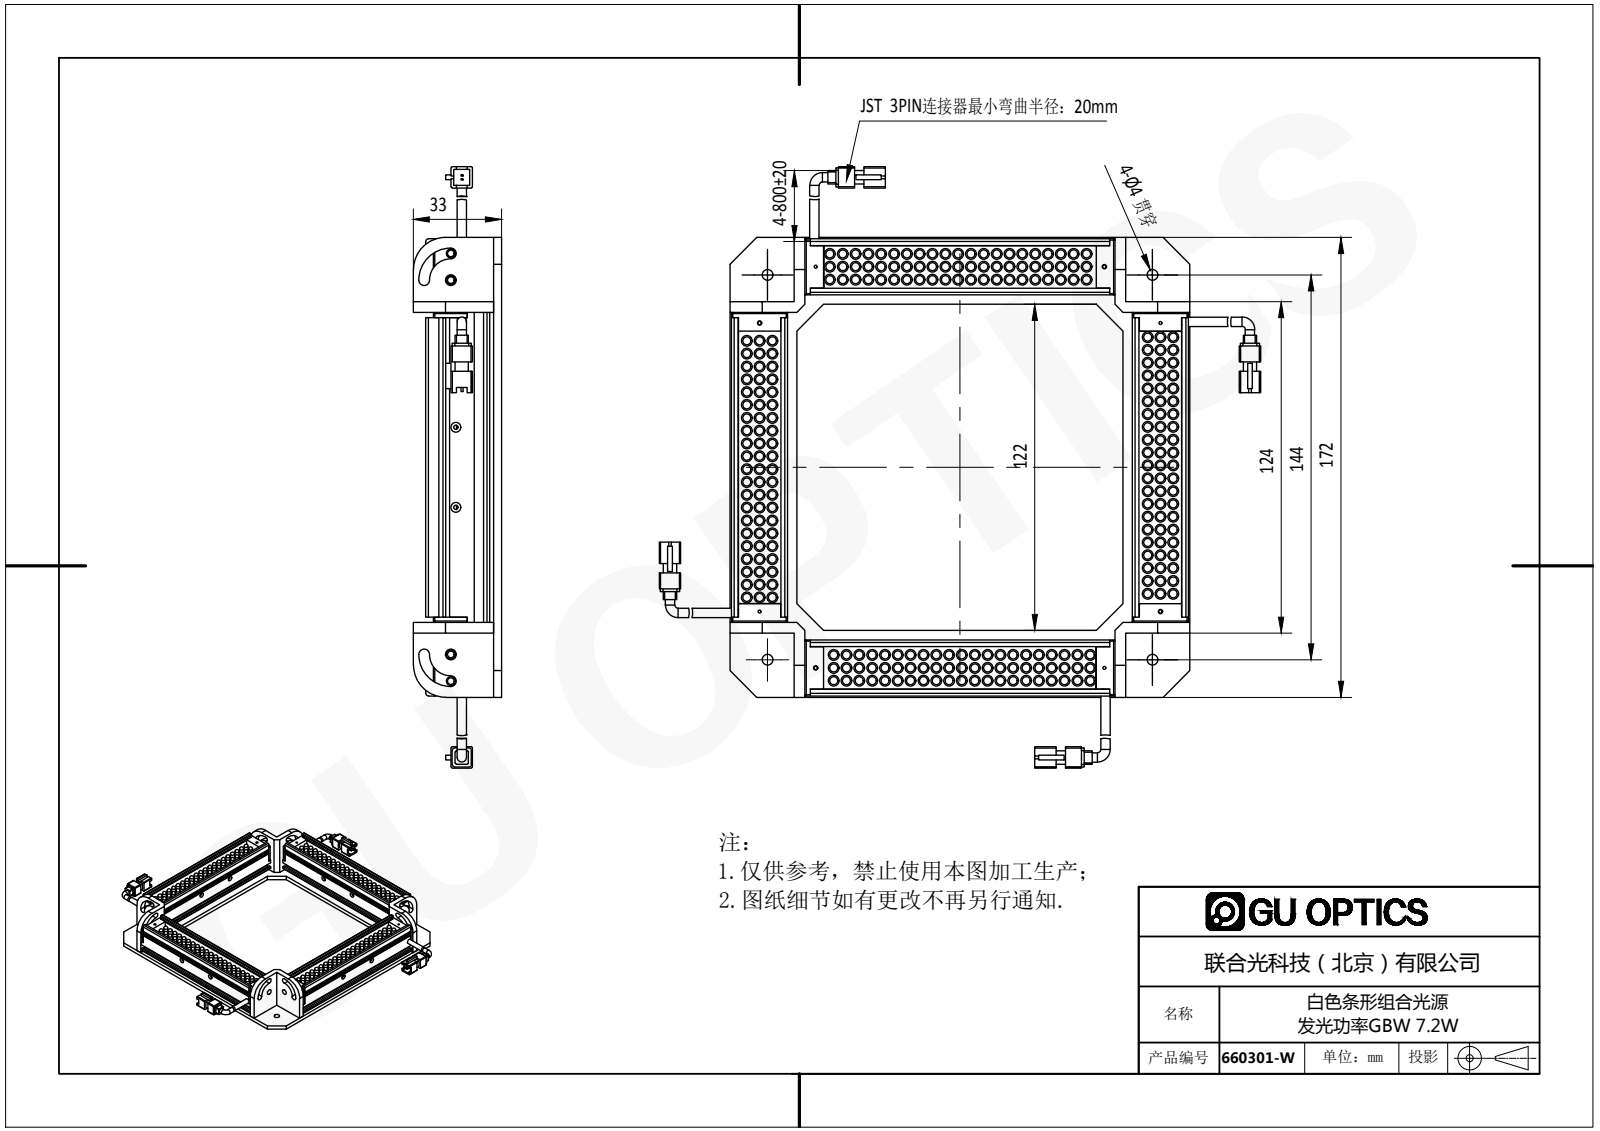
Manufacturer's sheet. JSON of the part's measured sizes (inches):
{"part_name": "660301-W", "step_written_by": "SolidWorks 2016 (AUTOMOTIVE_DESIGN)", "units": "inches", "bodies": {"solids": 29, "faces": 2961, "planar": 1092, "cylindrical": 1376, "other": 493}, "overall_size": [8.858, 8.858, 1.299], "volume_in3": 11.24, "surface_area_in2": 259.9, "round_holes": [[0.063, 12], [0.098, 8], [0.118, 8], [0.157, 8], [0.043, 4], [0.049, 4], [0.067, 4], [0.079, 4]], "round_bosses_or_shafts": [[0.157, 252], [0.118, 252], [0.138, 8]], "partial_cylinders_radius": [[0.039, 48], [0.02, 32], [0.079, 8], [0.472, 8], [0.065, 4], [0.315, 4]], "face_to_face_distances": [0.098, 0.118, 0.728, 5.906, 0.157, 0.827, 5.807, 0.039, 0.39, 0.256], "hole_center_spacings": [0.645, 0.719, 1.033, 4.252, 4.884, 4.962, 5.146, 5.278]}
